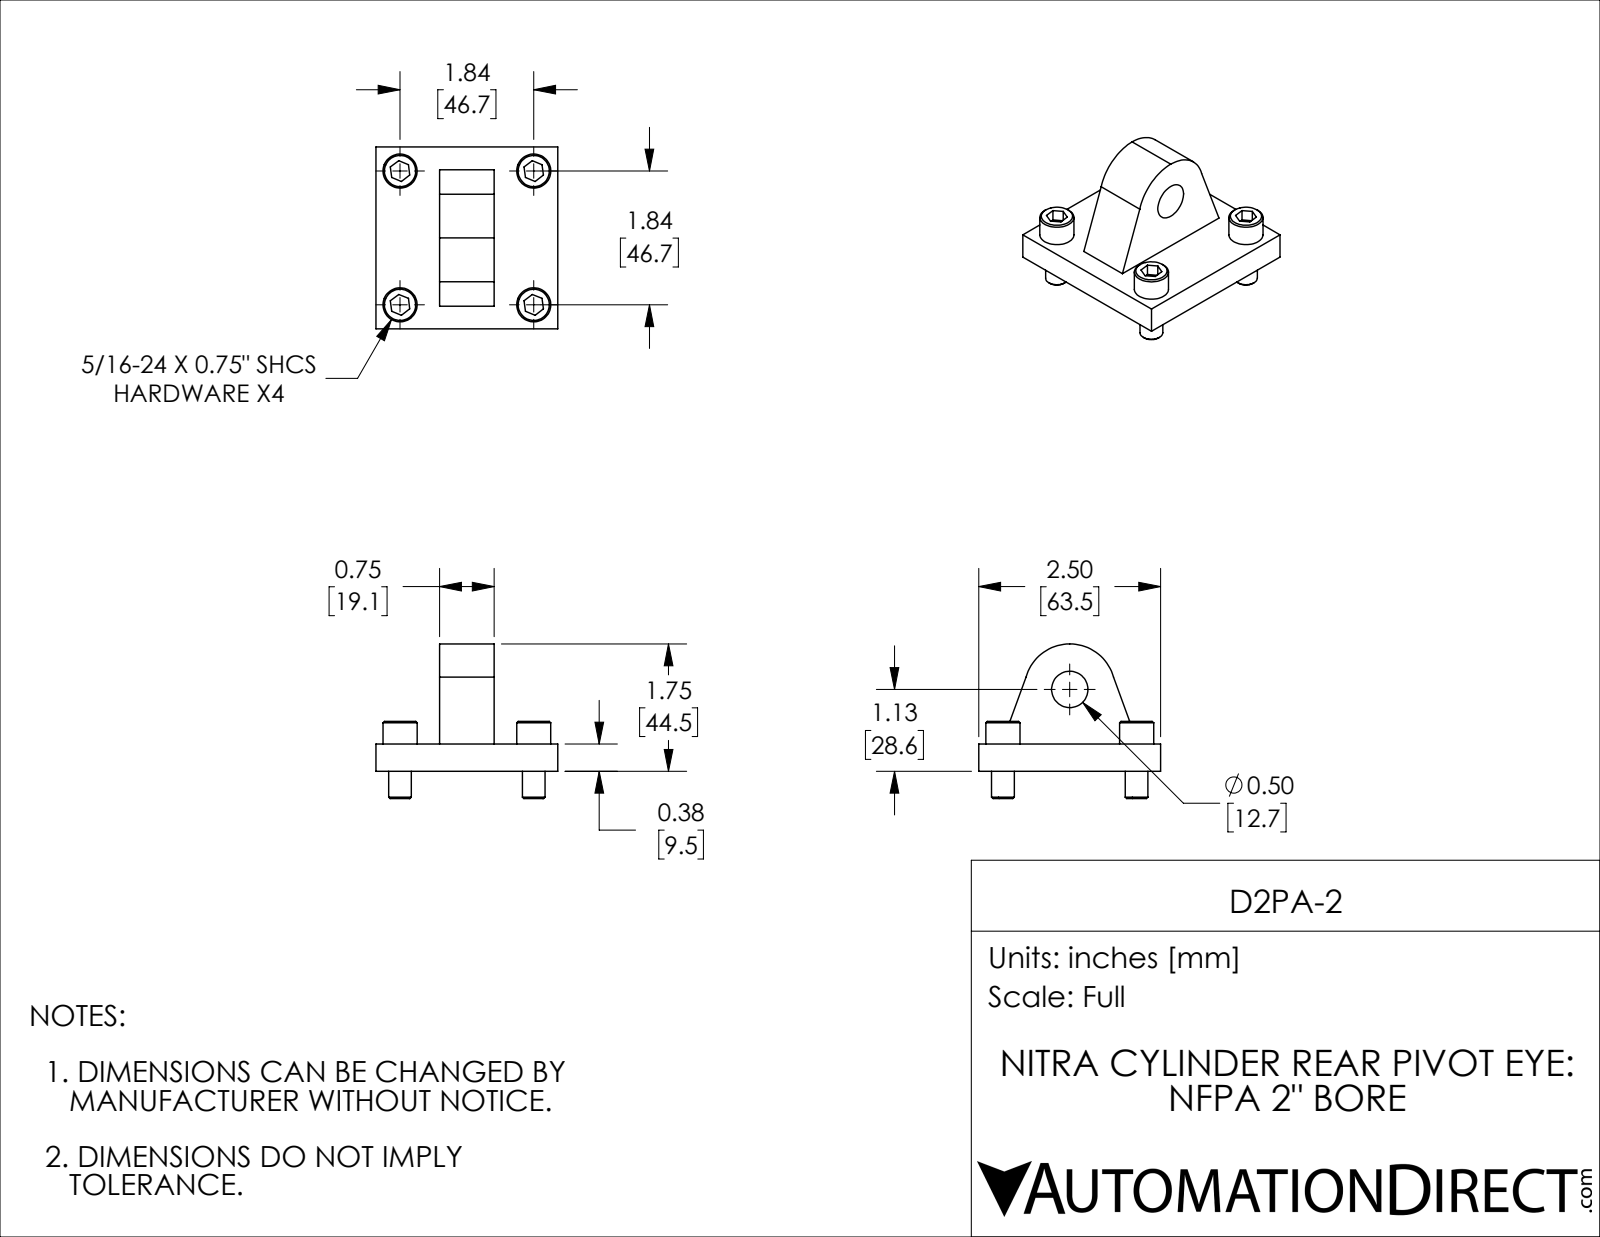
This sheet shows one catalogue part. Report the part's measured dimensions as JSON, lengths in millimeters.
{"part_name": "D2PA-2", "step_written_by": "SolidWorks 2019 (CONFIG_CONTROL_DESIGN)", "units": "millimeters", "bodies": {"solids": 5, "faces": 94, "planar": 50, "cylindrical": 28, "other": 16}, "overall_size": [63.5, 63.5, 54], "volume_mm3": 62780, "surface_area_mm2": 18970, "round_holes": [[8.7, 4], [12.7, 1]], "round_bosses_or_shafts": [[11.9, 4], [7.9, 4]], "partial_cylinders_radius": [[15.9, 1]], "face_to_face_distances": [9.5, 22.2, 41.3, 63.5, 19.1, 4, 7.9, 17.4, 6.4, 27], "hole_center_spacings": [46.7, 66]}
